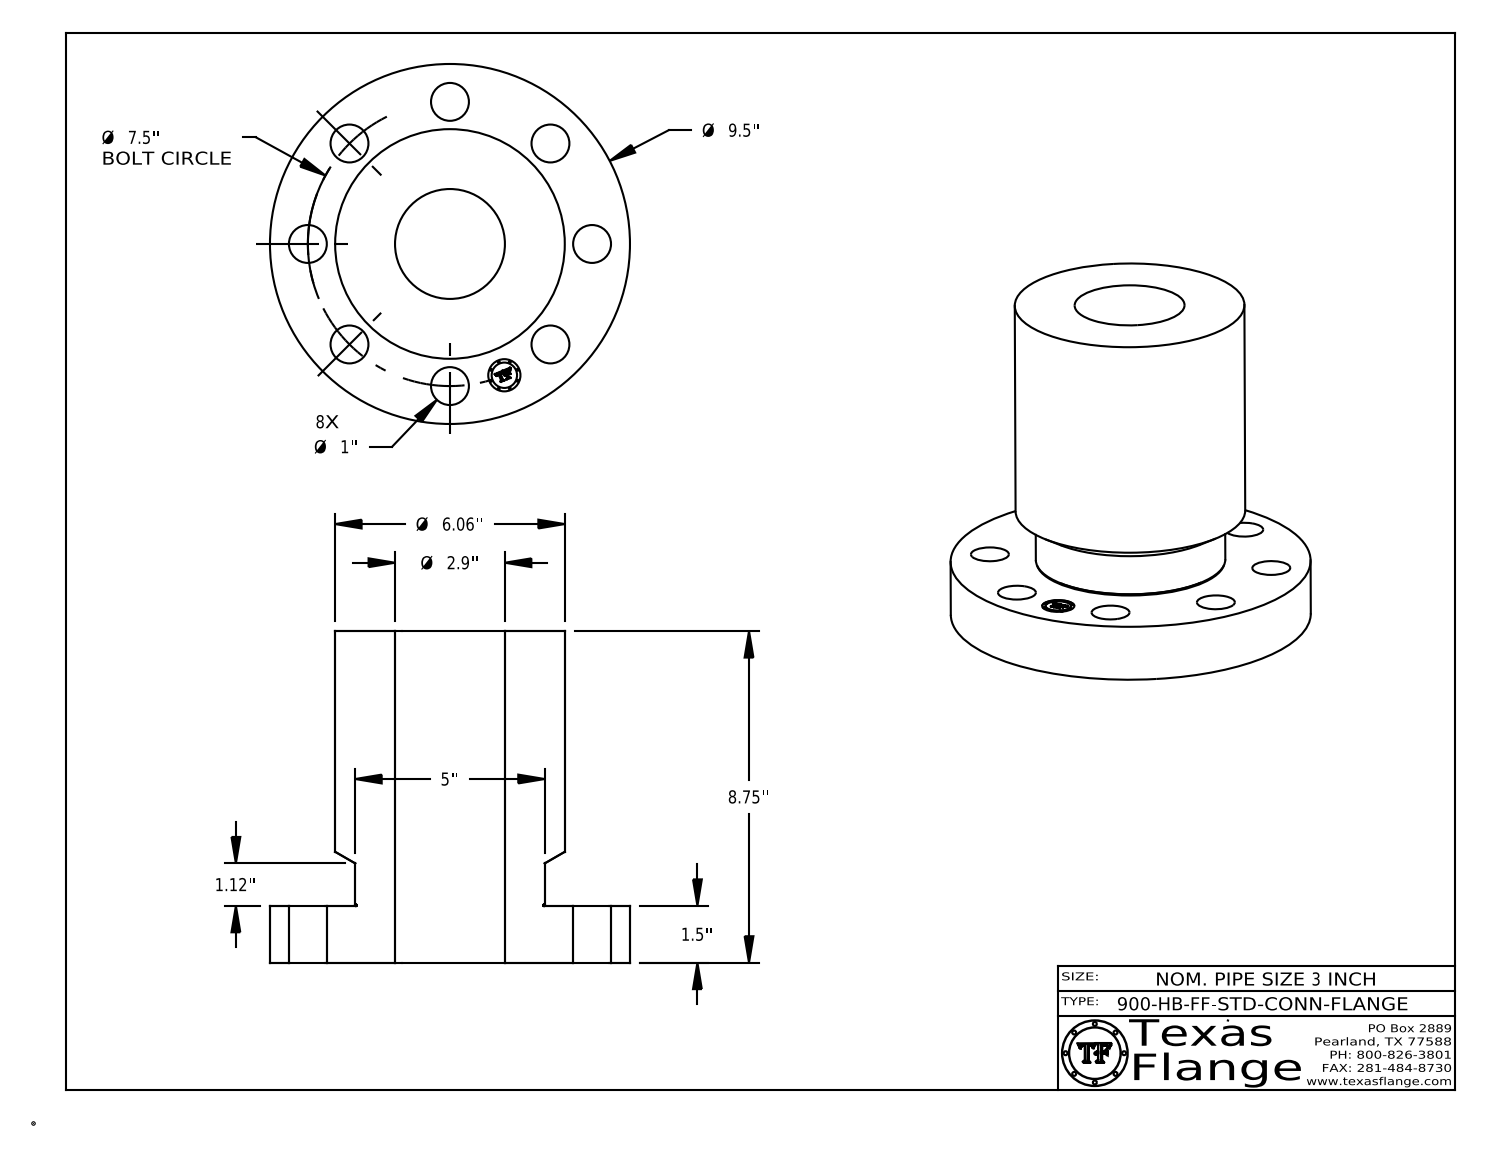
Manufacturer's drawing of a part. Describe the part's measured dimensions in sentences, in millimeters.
The part is named "3-900-HB-FF-STD-CONN-FLANGE". Its 3-D file was written by "CATIA V5 STEP AP214 (AUTOMOTIVE_DESIGN)". It is 1 solid with 418 faces: 368 planar, 44 cylindrical and 6 other. Overall it measures 241.3 by 241.3 by 222.3 millimeters. Its volume is 3 874 000 cubic millimeters and its surface area 275 500 square millimeters. Round holes: 8 of diameter 25.4, 1 of diameter 21.6, 1 of diameter 73.7. Round bosses or shafts: 8 of diameter 1.3, 1 of diameter 241.3, 1 of diameter 153.9, 1 of diameter 127, 1 of diameter 17. The main face-to-face distances are 38.1, 222.3, 184.2, 38, 184.3, 6.5, 6.3, 1.2, 4.2, 5.4. The hole center spacings are 95.3, 72.9, 134.7, 176, 37.2, 158.4, 186.8, 190.5.
